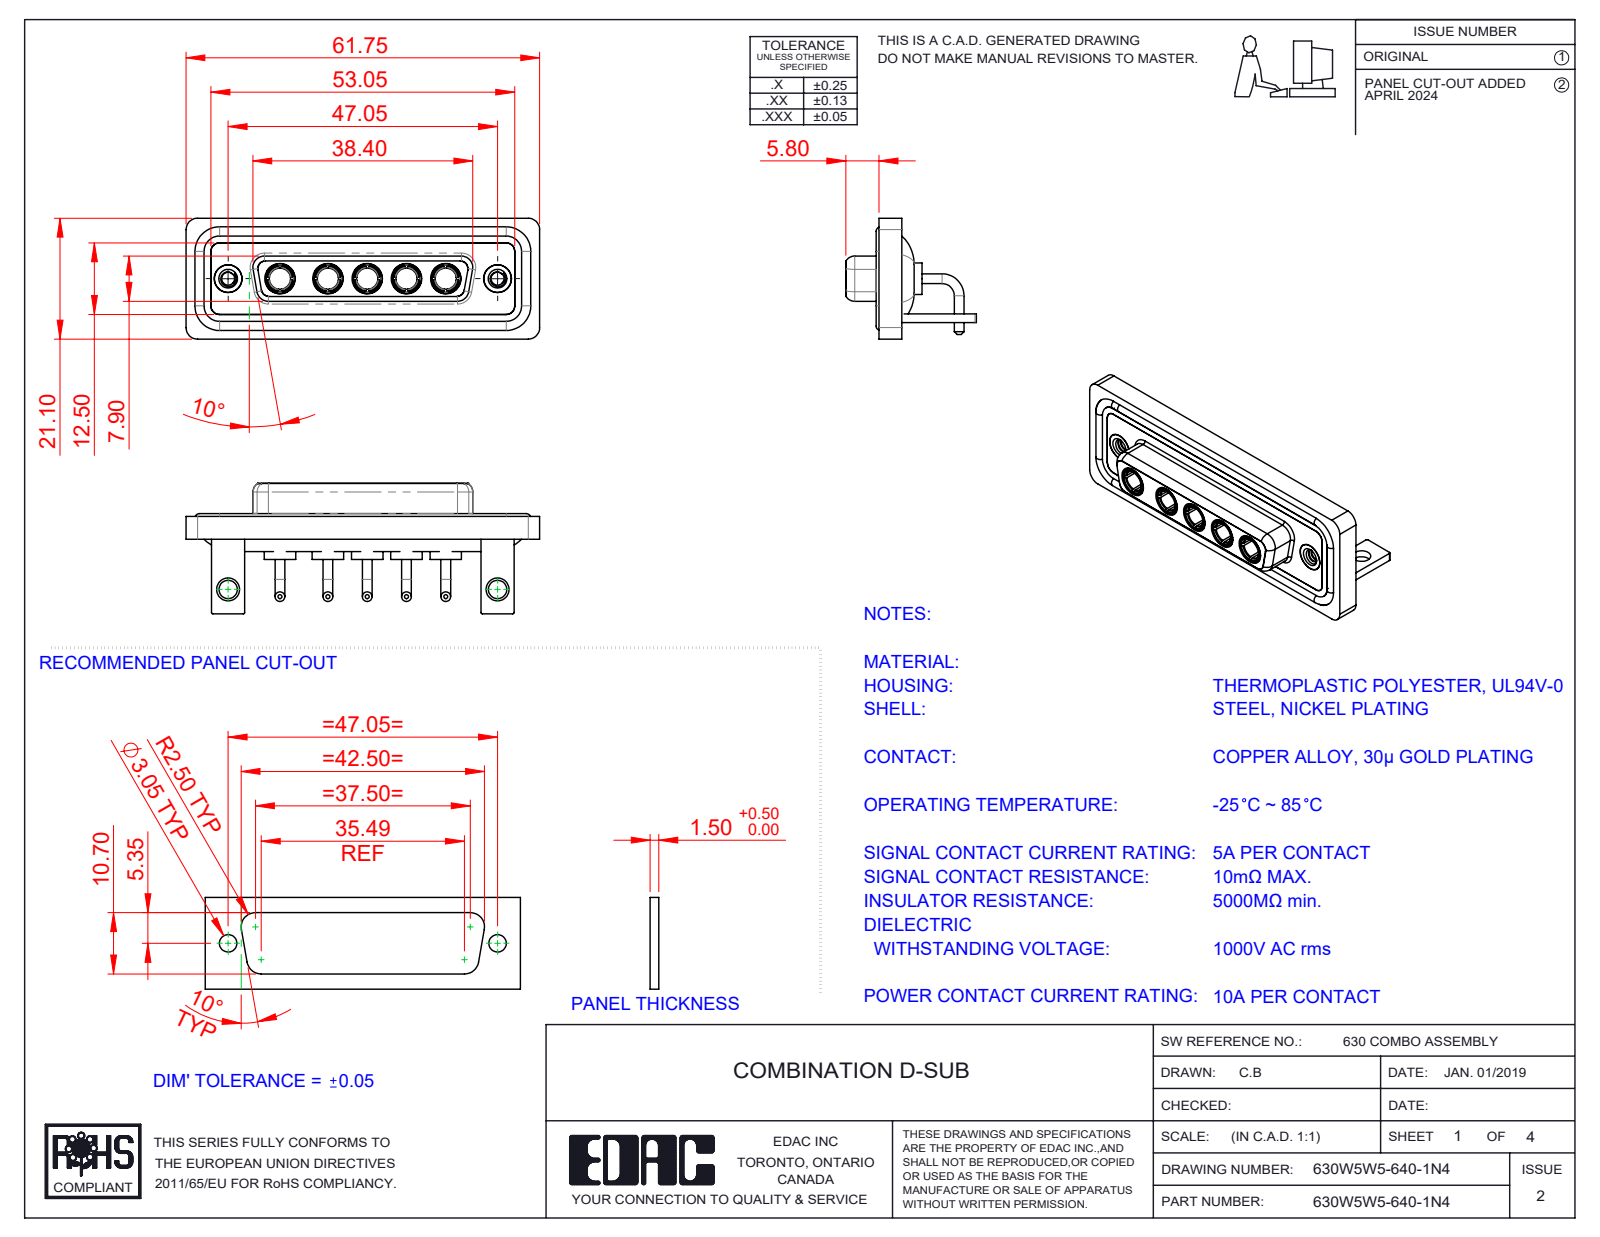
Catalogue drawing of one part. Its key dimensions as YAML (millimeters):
part_name: "630Combo Threaded Rivet_2; 630W5W5-640-1N4; 630Combo Shell Front_25 Contacts; 630Combo Shell Rear_25 Contacts (+4 more)"
step_written_by: "SolidWorks 2023 (CONFIG_CONTROL_DESIGN)"
units: millimeters
bodies: {solids: 19, faces: 824, planar: 270, cylindrical: 337, other: 217}
overall_size: [61.75, 22.8, 21.1]
volume: 8513
surface_area: 14295
round_holes:
  - {diameter: 4.85, count: 7}
  - {diameter: 3.7, count: 5}
  - {diameter: 5.3, count: 5}
  - {diameter: 2.26, count: 2}
  - {diameter: 3.2, count: 2}
  - {diameter: 4, count: 2}
  - {diameter: 4.05, count: 2}
  - {diameter: 5, count: 2}
round_bosses_or_shafts:
  - {diameter: 1.7, count: 10}
  - {diameter: 5.5, count: 5}
  - {diameter: 5.2, count: 5}
  - {diameter: 4.96, count: 5}
  - {diameter: 4.75, count: 5}
  - {diameter: 3.75, count: 5}
  - {diameter: 1.6, count: 4}
  - {diameter: 4.95, count: 2}
partial_cylinders:
  - {radius: 2, count: 19}
  - {radius: 1.5, count: 18}
  - {radius: 0.25, count: 16}
  - {radius: 1.35, count: 8}
  - {radius: 1.6, count: 8}
  - {radius: 0.5, count: 5}
  - {radius: 2.1, count: 5}
  - {radius: 0.6, count: 4}
face_to_face_distances: [0.4, 1.8, 1.5, 2.9, 3.7, 4.1, 1.1, 1.4, 1.6, 2.5]
hole_center_spacings: [6.86, 9.04, 38.01, 47.05, 6.87, 8.38, 13.72, 13.73]
